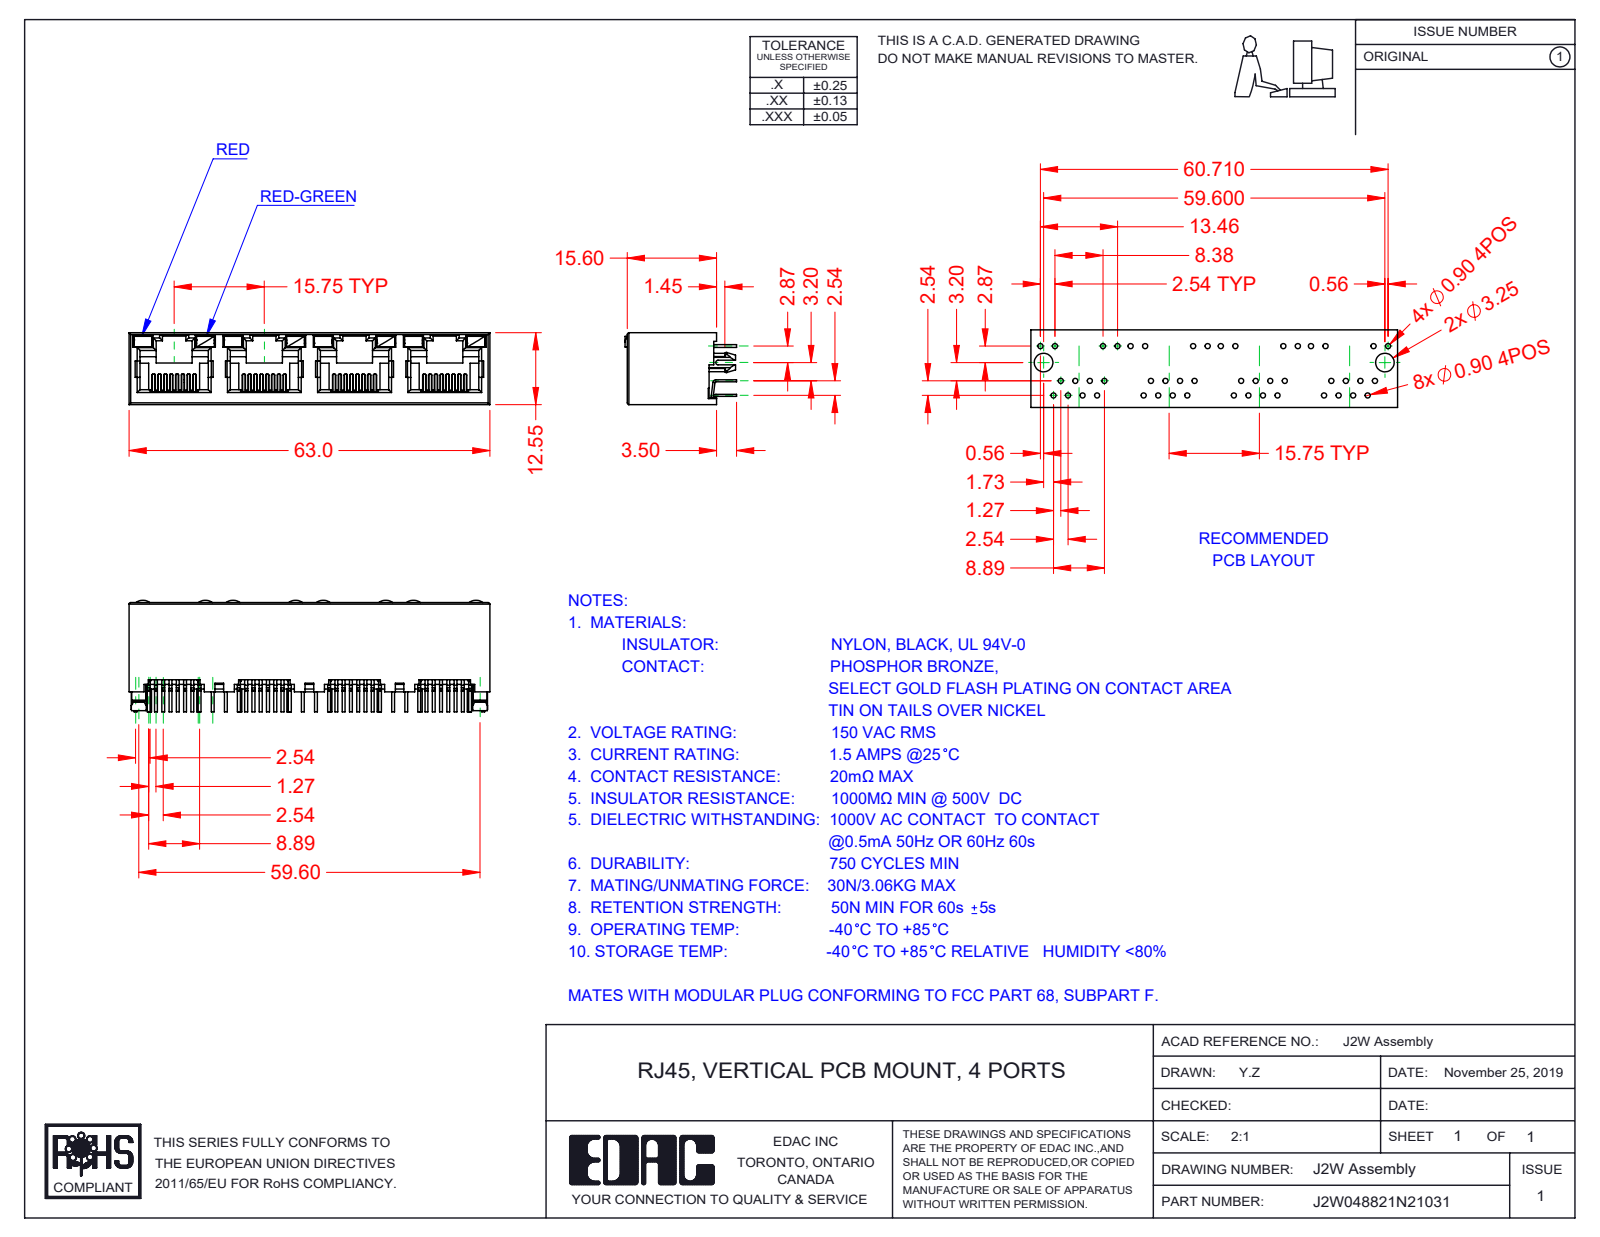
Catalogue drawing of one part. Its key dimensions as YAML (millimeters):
part_name: "J2W048821N26131; 2W Contacts; 2W LED LH_2-Red; 2W LED RH_6-Red-Green (+2 more)"
step_written_by: "SolidWorks 2016 (CONFIG_CONTROL_DESIGN)"
units: millimeters
bodies: {solids: 45, faces: 3139, planar: 2600, cylindrical: 481, other: 58}
overall_size: [63, 19.5, 12.55]
volume: 5335
surface_area: 13144
partial_cylinders:
  - {radius: 0.15, count: 64}
  - {radius: 0.2, count: 29}
  - {radius: 0.5, count: 28}
  - {radius: 0.3, count: 14}
  - {radius: 0.45, count: 8}
  - {radius: 2, count: 8}
  - {radius: 0.25, count: 2}
  - {radius: 1.5, count: 2}
face_to_face_distances: [12.55, 11.9, 0.65, 15.75, 0.36, 1.5, 0.78, 0.6, 11.3, 31.5]
